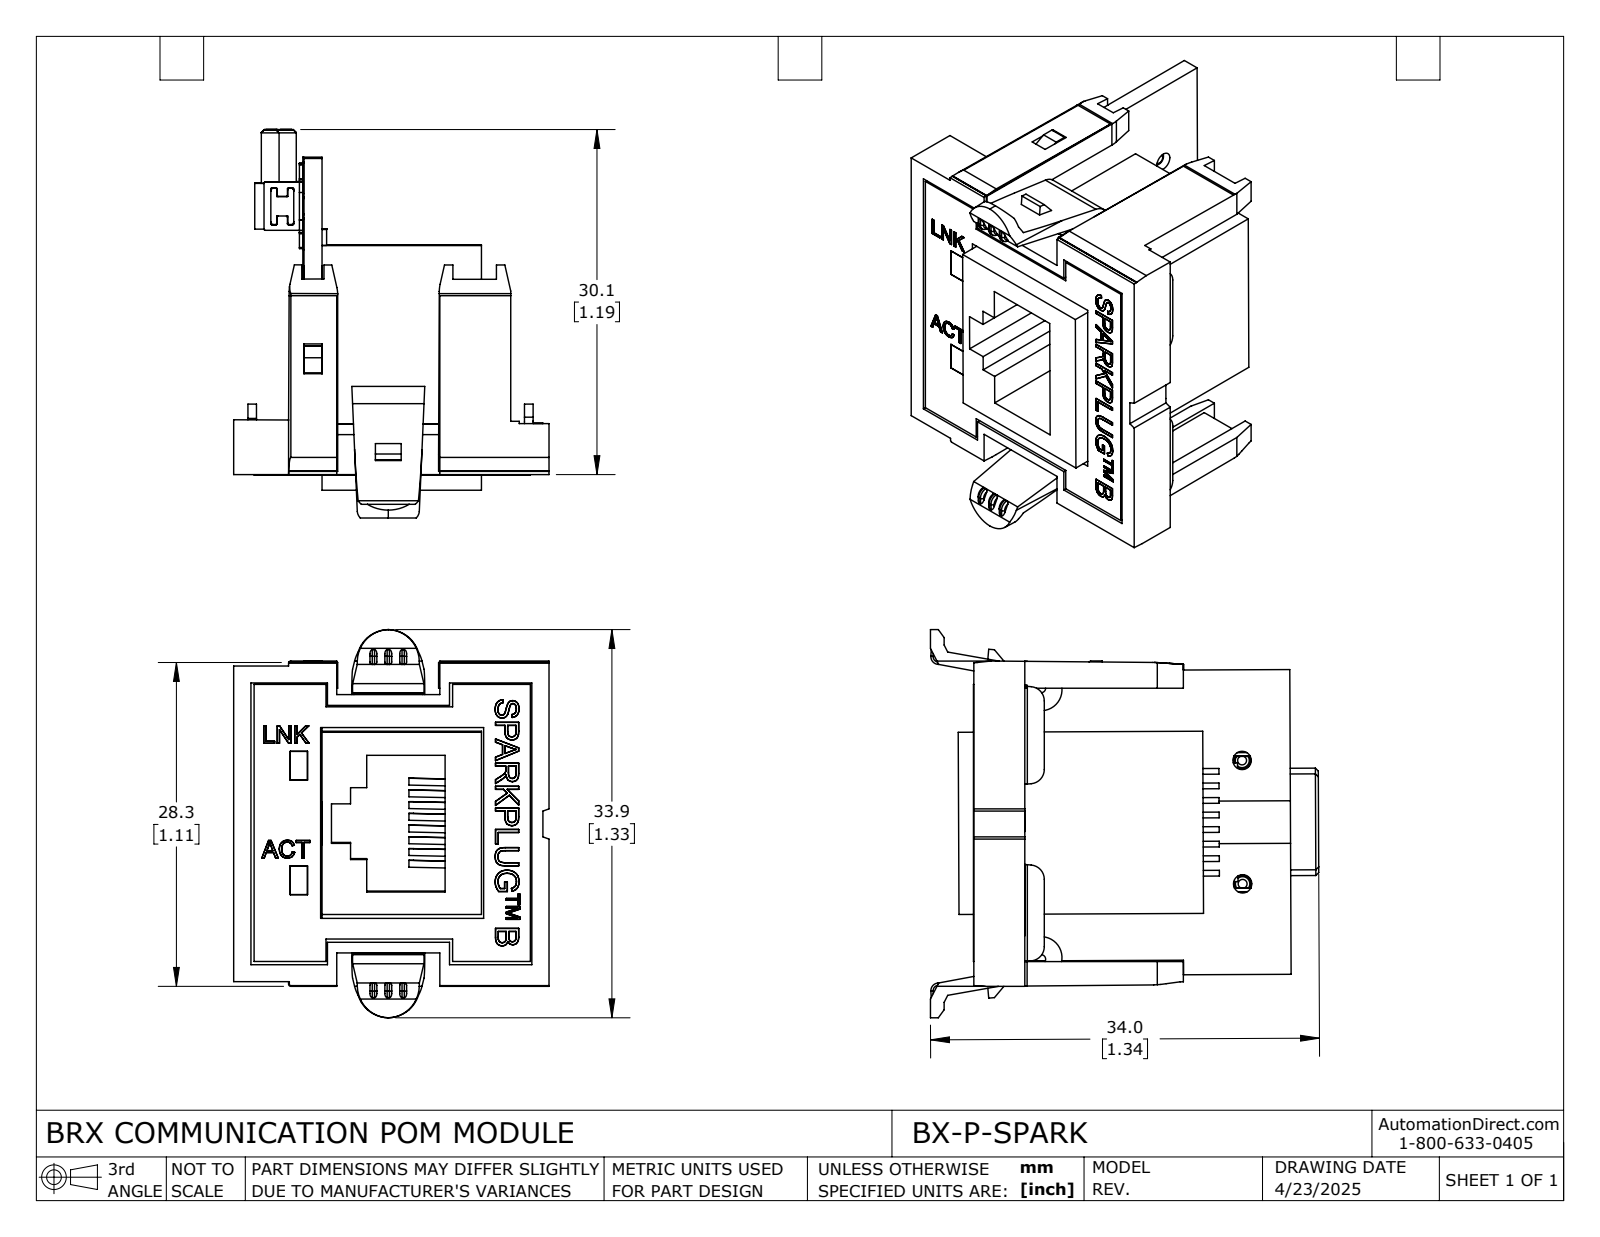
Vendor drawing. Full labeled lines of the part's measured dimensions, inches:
Part name (STEP PRODUCT): BX-P-SPARK
STEP written by: SolidWorks 2021 (AUTOMOTIVE_DESIGN)
Units: inches
Bodies: 34 solids, 1906 faces (1408 planar, 159 cylindrical, 339 other)
Overall size (bounding box): 1.335 × 1.334 × 1.084
Volume: 0.393 in³ · Surface area: 14.53 in²
Round holes (diameter × count): ⌀0.037 ×3, ⌀0.063 ×2
Round bosses / shafts (diameter × count): ⌀0.118 ×2
Partial cylindrical surfaces — rounded edges, fillets, slot ends (radius × count): R0.004 ×40, R0.008 ×27, R0.006 ×8, R0.049 ×5, R0.01 ×4, R0.108 ×4, R0.02 ×3, R0.03 ×3
Main face-to-face distances: 0.02, 0.062, 0.61, 0.548, 0.626, 0.066, 0.021, 0.066, 0.485, 0.423
Hole centre spacings: 0.552, 0.687, 0.196, 0.197, 0.394, 0.424, 0.591, 0.592
